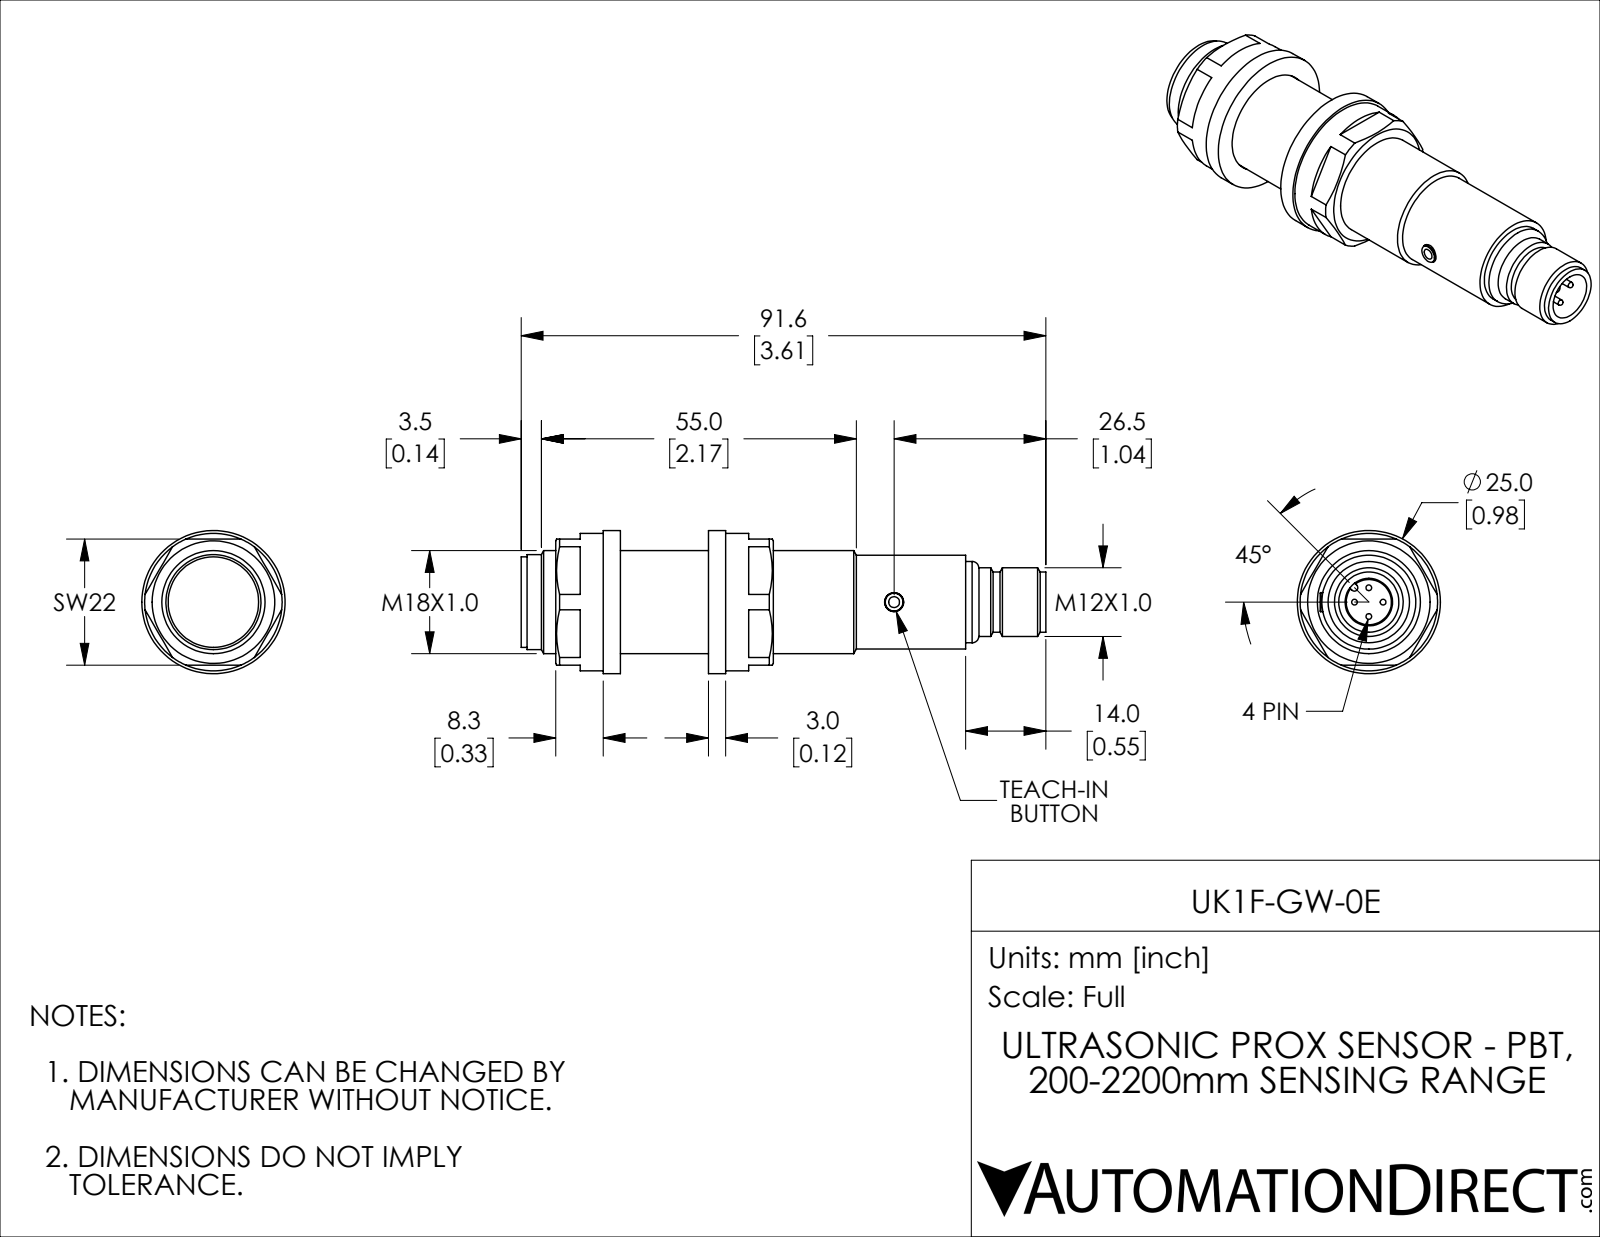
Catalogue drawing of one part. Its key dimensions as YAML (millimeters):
part_name: "UK1F-GW-0E"
step_written_by: "SolidWorks 2018 (AUTOMOTIVE_DESIGN)"
units: millimeters
bodies: {solids: 6, faces: 123, planar: 43, cylindrical: 49, other: 31}
overall_size: [91.6, 25, 25]
volume: 24200
surface_area: 10330
round_holes:
  - {diameter: 3.3, count: 1}
  - {diameter: 8.3, count: 1}
  - {diameter: 18, count: 1}
  - {diameter: 18.2, count: 1}
round_bosses_or_shafts:
  - {diameter: 1, count: 4}
  - {diameter: 25, count: 1}
  - {diameter: 24, count: 1}
  - {diameter: 16.6, count: 1}
  - {diameter: 16.4, count: 1}
  - {diameter: 15.8, count: 1}
  - {diameter: 14.2, count: 1}
  - {diameter: 12, count: 1}
partial_cylinders:
  - {radius: 0.6, count: 1}
face_to_face_distances: [3, 18.4, 21.4, 15.4, 22, 8.3, 11.3, 26.7, 29.7, 14.3]
